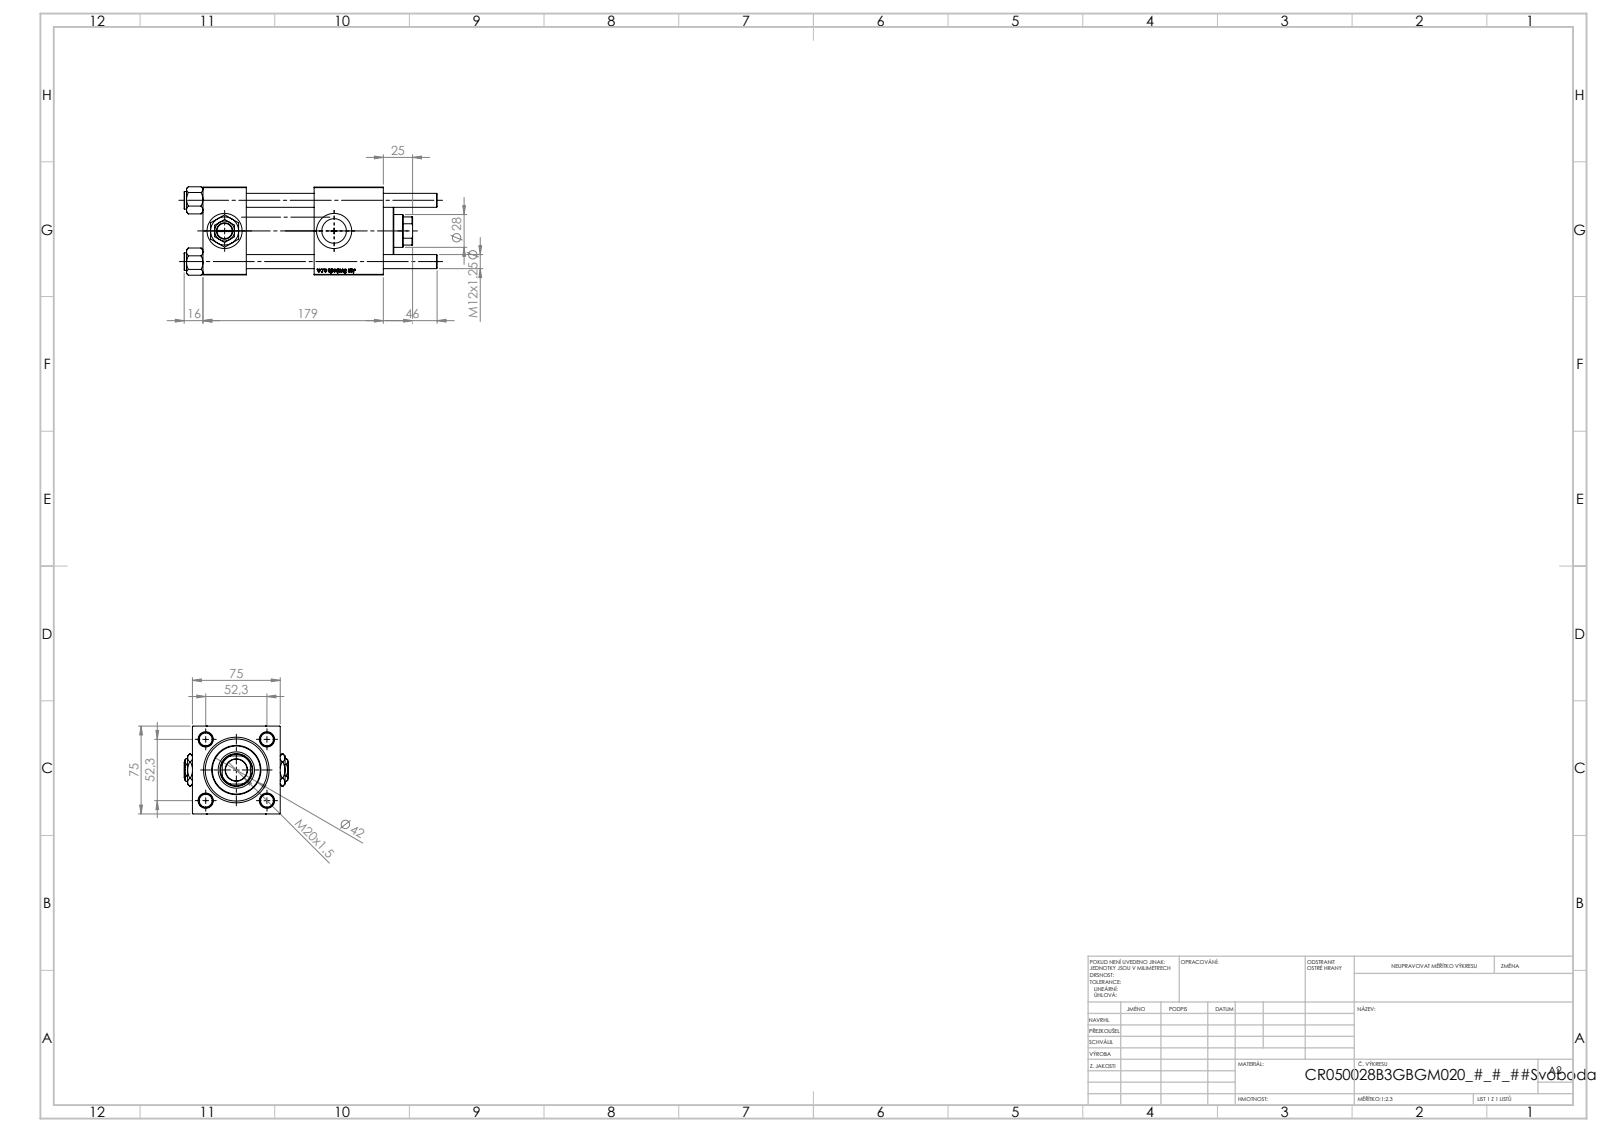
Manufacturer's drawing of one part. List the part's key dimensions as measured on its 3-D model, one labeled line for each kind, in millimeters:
Part name (STEP PRODUCT): V215_VC_A; V215CR_B-1; NUT_M5_B; V215CR_VCP_B (+2 more)
STEP written by: SolidWorks 2019 (CONFIG_CONTROL_DESIGN)
Units: millimetres
Bodies: 13 solids, 1257 faces (479 planar, 88 cylindrical, 690 other)
Overall size (bounding box): 216 × 89 × 75.45
Volume: 697 144 mm³ · Surface area: 171 614 mm²
Round holes (diameter × count): ⌀12 ×4, ⌀7 ×2, ⌀20.96 ×2, ⌀30 ×2, ⌀18.5 ×1, ⌀28 ×1, ⌀31 ×1, ⌀41 ×1, ⌀50 ×1, ⌀53 ×1
Round bosses / shafts (diameter × count): ⌀15 ×4, ⌀56 ×1, ⌀42 ×1
Partial cylindrical surfaces — rounded edges, fillets, slot ends (radius × count): R13.5 ×1
Main face-to-face distances: 75, 37, 154, 117, 95, 58, 59, 125.3, 88.3, 30.3
Hole centre spacings: 36.98, 52.3, 73.96, 93.5
